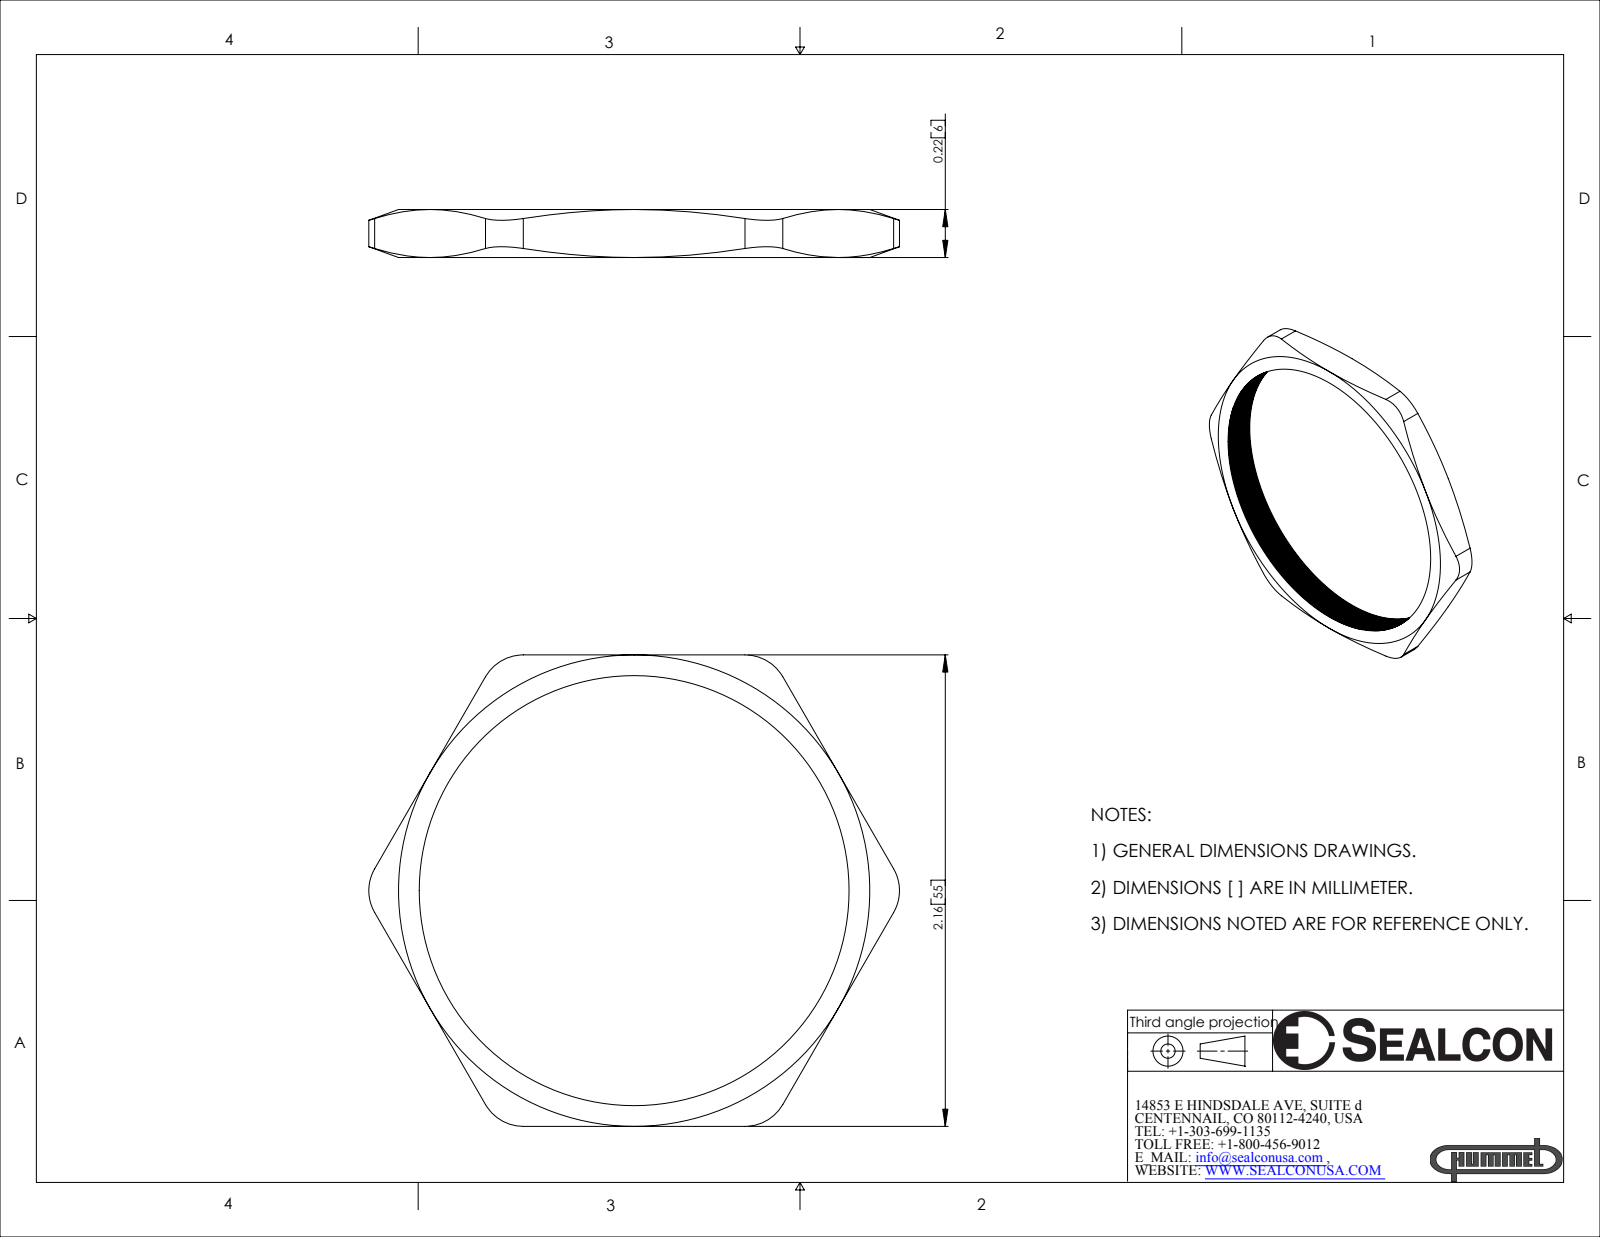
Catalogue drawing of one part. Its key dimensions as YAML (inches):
part_name: "NM-50-BR"
step_written_by: "SolidWorks 2007 (CONFIG_CONTROL_DESIGN)"
units: inches
bodies: {solids: 1, faces: 137, planar: 8, cylindrical: 7, other: 122}
overall_size: [2.432, 2.16, 0.22]
volume: 0.187
surface_area: 6.032
partial_cylinders:
  - {radius: 0.2, count: 6}
face_to_face_distances: [2.16, 0.22]
